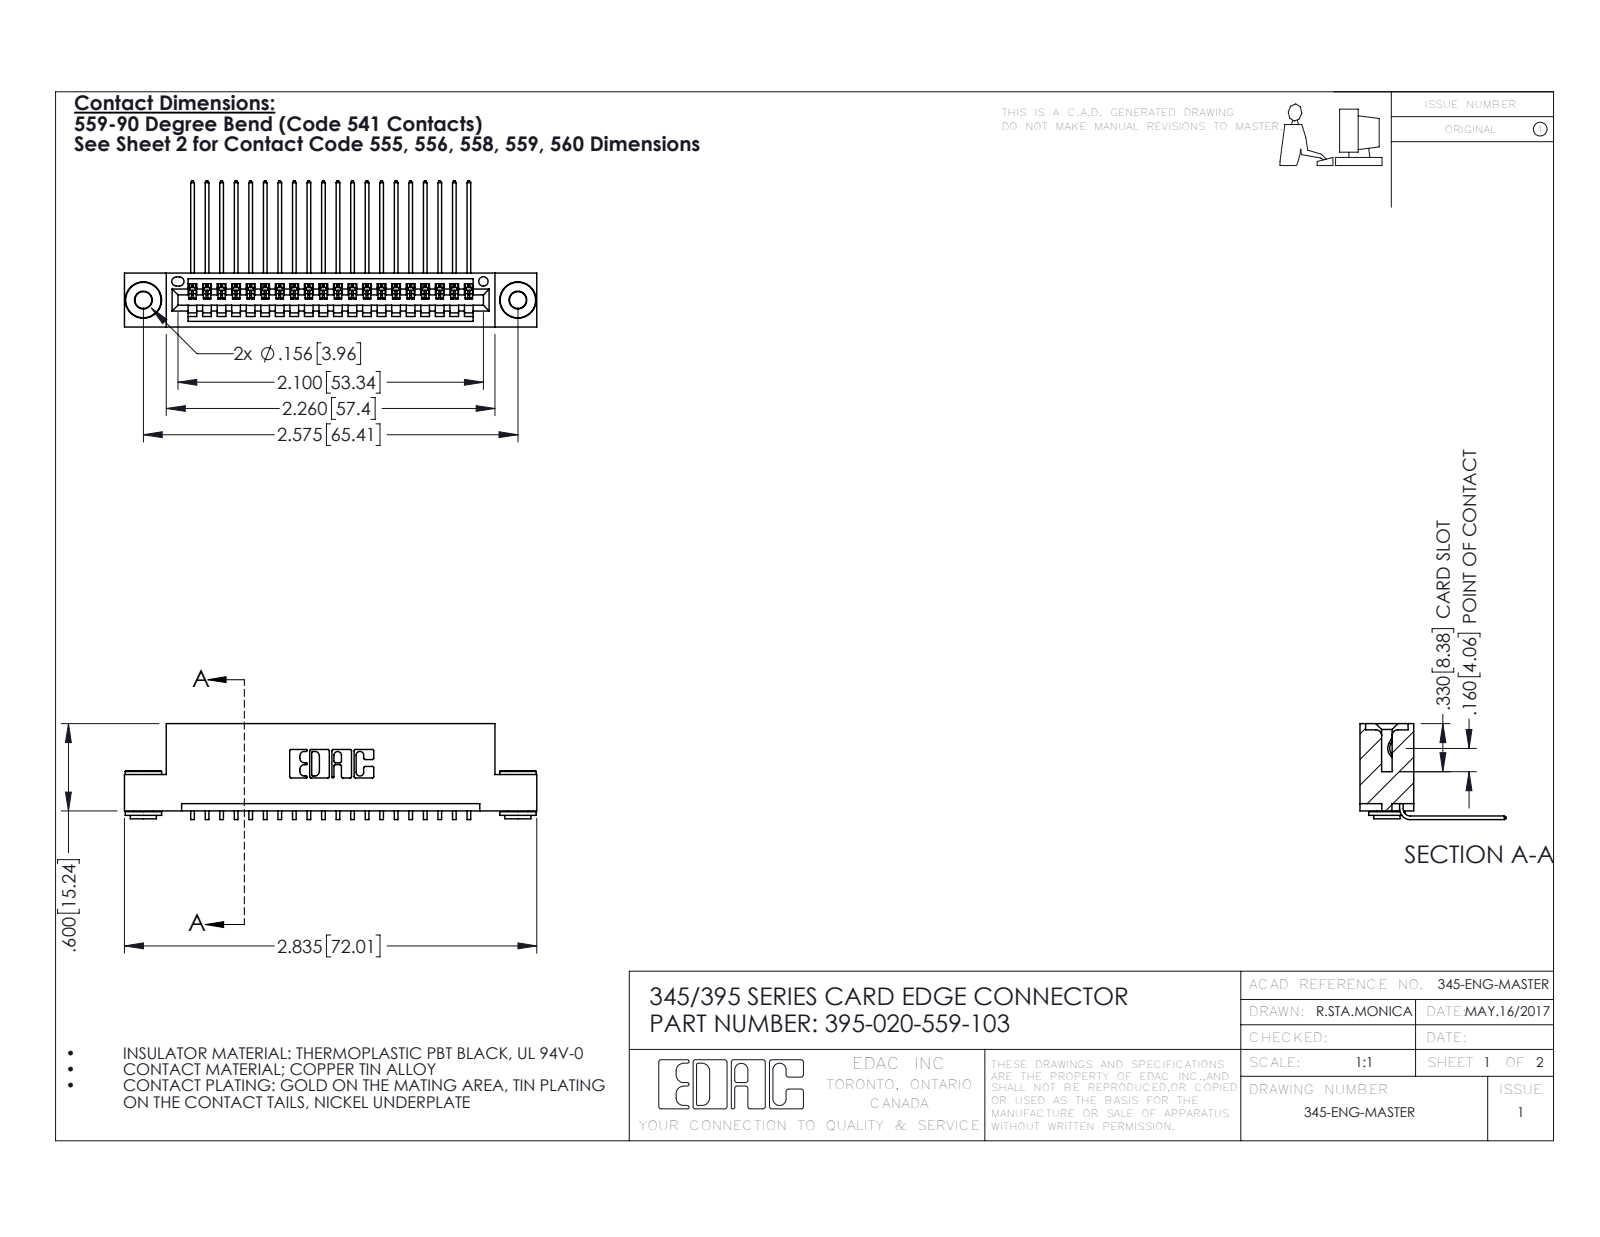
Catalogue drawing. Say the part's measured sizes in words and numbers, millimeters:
The part is named "395-020-559-103; 345 Part_Flush Mounting Lugs - 0.156 Dia-TH; 345-292-001_558 559 Tail - 1; 345-250-002_345-250-002-102". Its 3-D file was written by "SolidWorks 2016 (CONFIG_CONTROL_DESIGN)". It is 23 solids with 1364 faces: 930 planar, 426 cylindrical and 8 other. Overall it measures 72 by 25.5 by 16.7 millimeters. Its volume is 6 750 cubic millimeters and its surface area 9 271 square millimeters. Round holes: 2 of diameter 2.9, 2 of diameter 4, 1 of diameter 1.6. Round bosses or shafts: 2 of diameter 6.4, 2 of diameter 4.6, 2 of diameter 3.5. Partial cylindrical surfaces (rounded edges, fillets, slot ends): 40 of radius 0.2, 22 of radius 0.3, 6 of radius 0.2, 6 of radius 0.8, 3 of radius 0.7, 2 of radius 0.8, 2 of radius 1, 1 of radius 0.4. The main face-to-face distances are 1.8, 7.6, 5.1, 9.4, 0.6, 2.5, 6.9, 5.7, 3.8, 15.2. The hole center spacings are 6.9, 59.5, 65.4.
